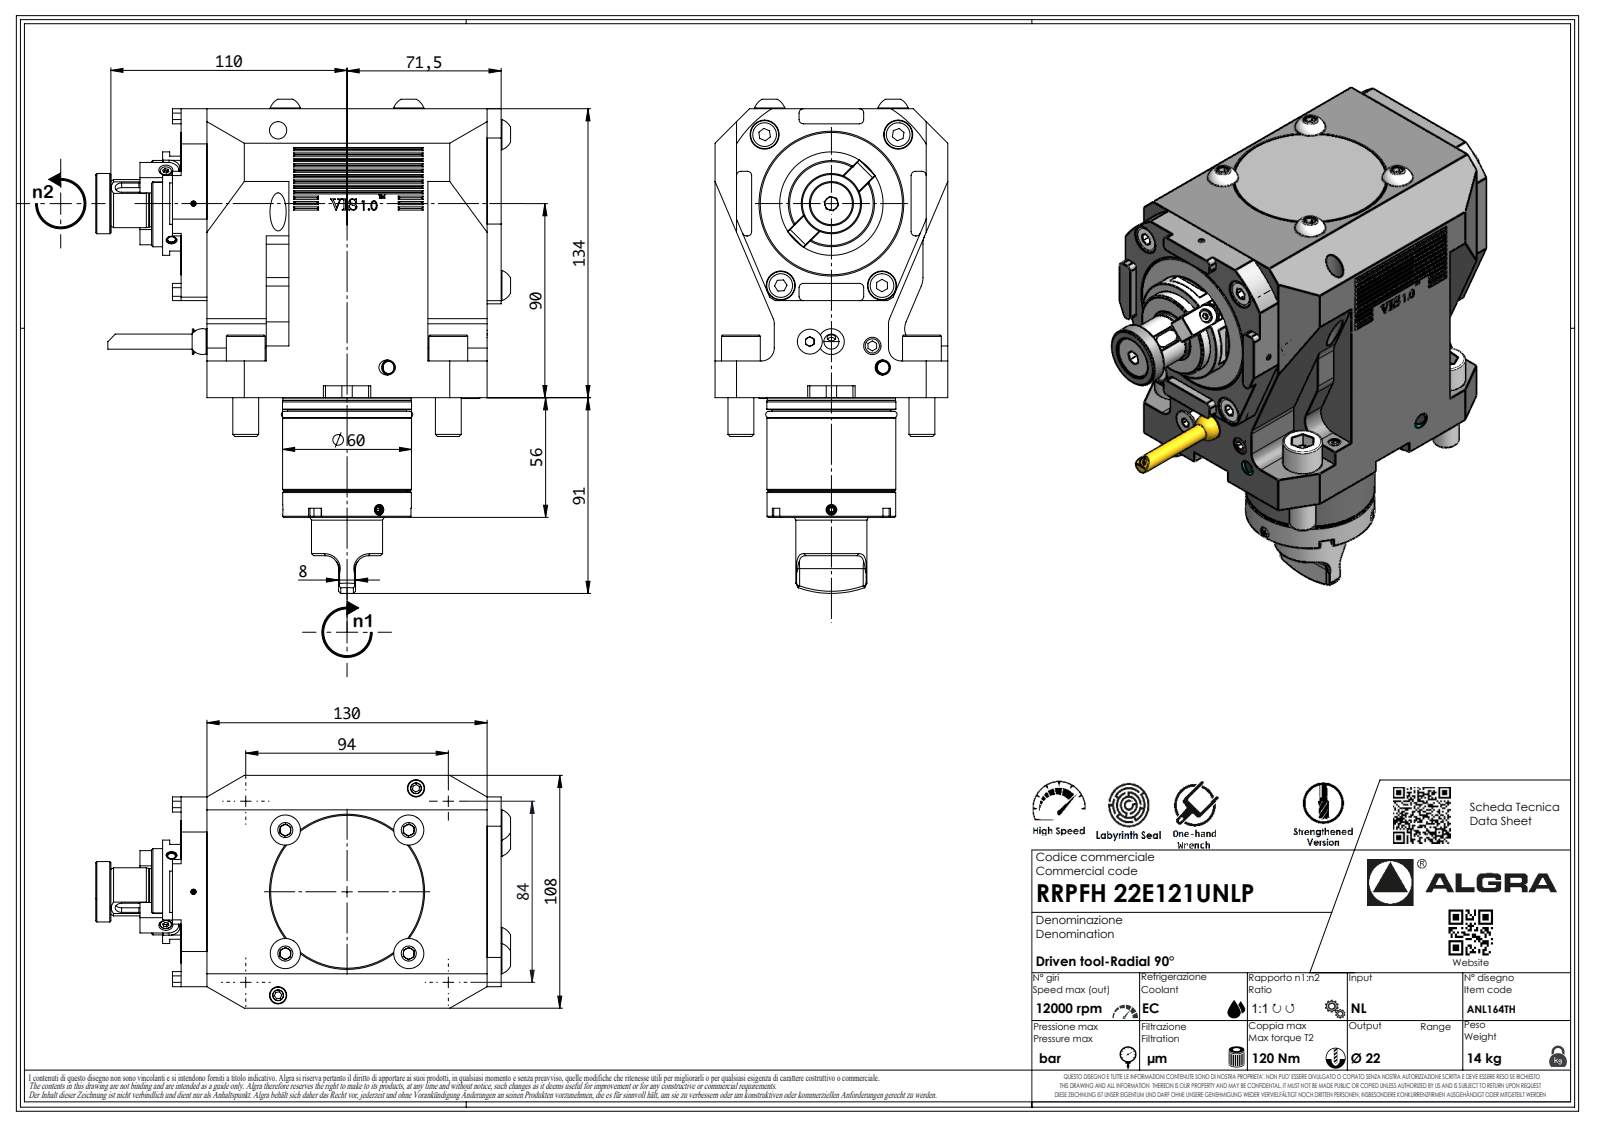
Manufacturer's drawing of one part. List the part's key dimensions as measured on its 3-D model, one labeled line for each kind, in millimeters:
Part name (STEP PRODUCT): RRPFH22E121UNLP
STEP written by: SolidWorks 2023 (AUTOMOTIVE_DESIGN)
Units: millimetres
Bodies: 1 solid, 999 faces (692 planar, 133 cylindrical, 174 other)
Overall size (bounding box): 224.8 × 188.1 × 108
Volume: 2 009 000 mm³ · Surface area: 126 734 mm²
Round holes (diameter × count): ⌀2.1 ×1
Round bosses / shafts (diameter × count): ⌀18 ×4, ⌀12 ×4, ⌀59.9 ×1, ⌀59.8 ×1, ⌀59.7 ×1, ⌀59.5 ×1, ⌀55.2 ×1, ⌀48 ×1
Partial cylindrical surfaces — rounded edges, fillets, slot ends (radius × count): R0.2 ×21, R8 ×18, R2 ×16, R6 ×10, R0.33 ×7, R0.52 ×7, R3.7 ×7, R10 ×4
Main face-to-face distances: 108, 134, 27.5, 12, 102.5, 6.5, 136.5, 39.5, 5.5, 148.5
